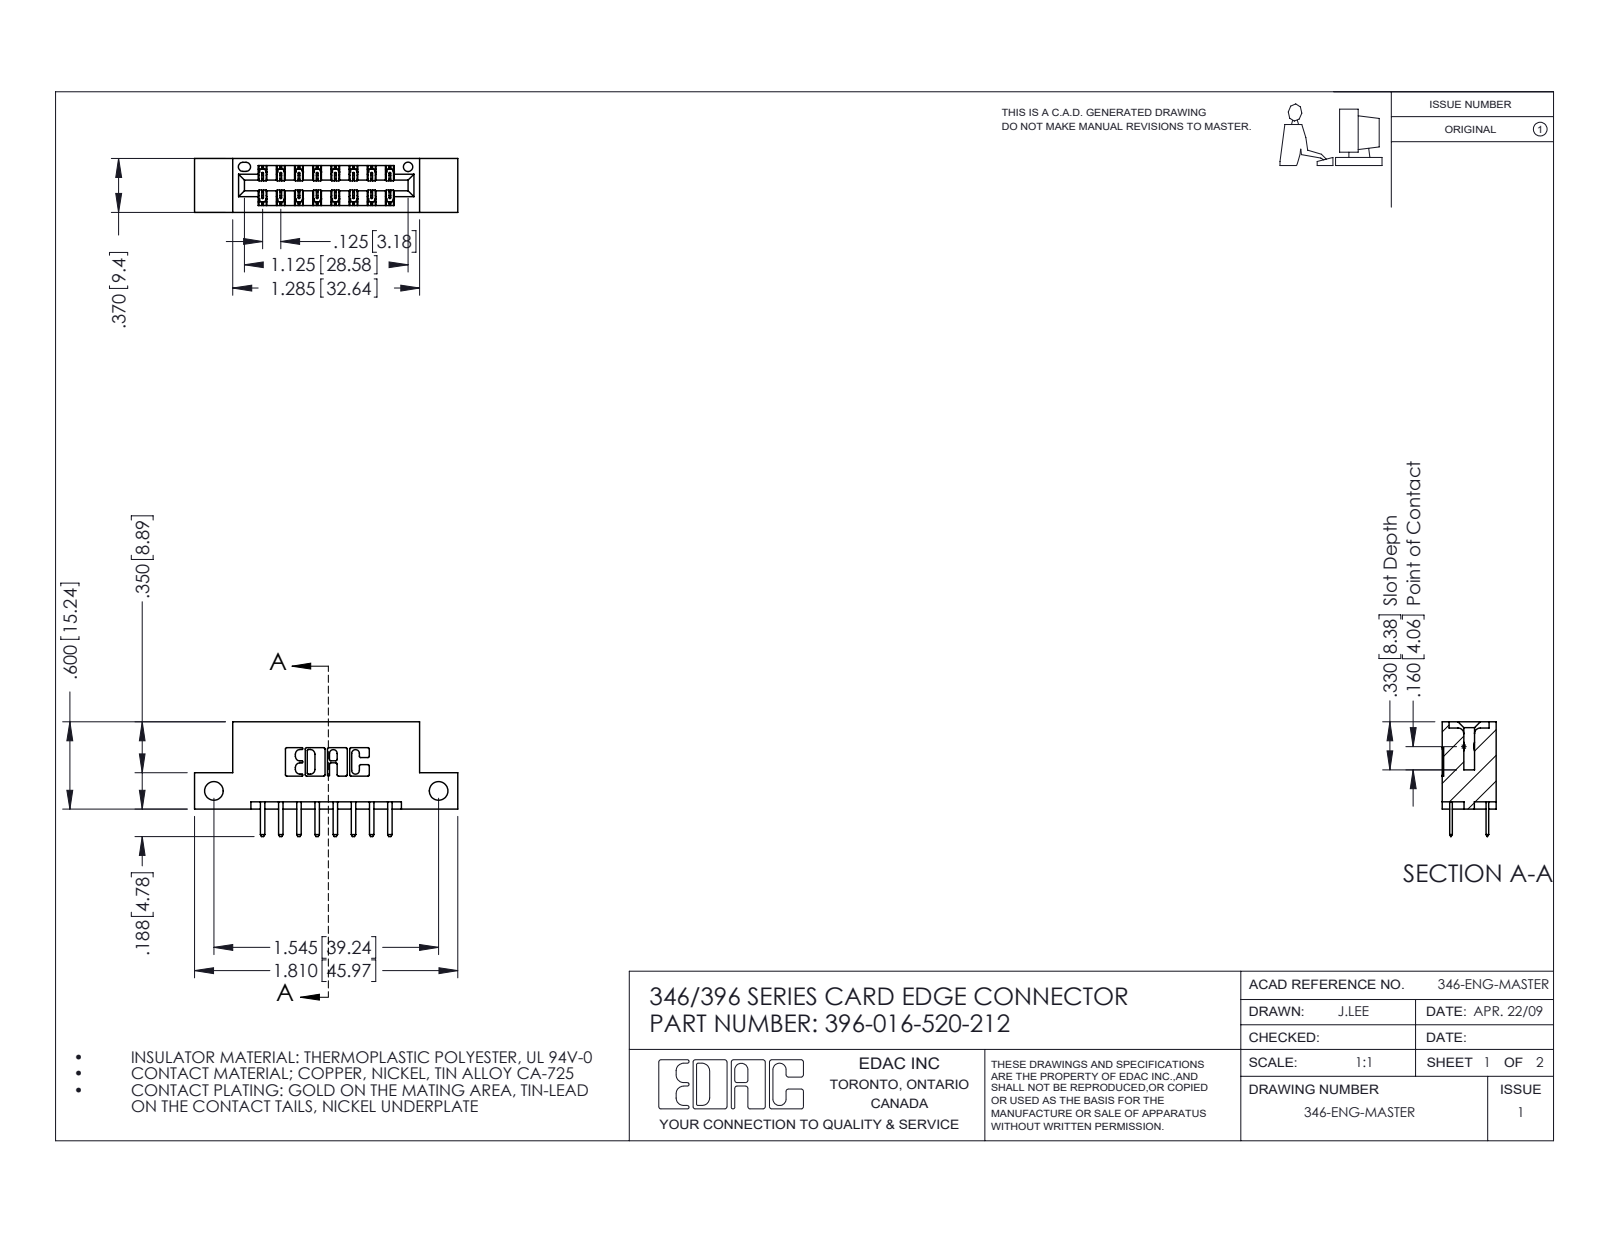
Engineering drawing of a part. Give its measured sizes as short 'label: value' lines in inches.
name: 396-016-520-212; 346 Part_Flush Mounting Lugs - Side Mount; 345-292-001_345-293-120
written by: SolidWorks 2016 (CONFIG_CONTROL_DESIGN)
unit: in
bodies: 17 solids, 1018 faces (668 planar, 350 cylindrical, 0 other)
size: 1.81 × 0.788 × 0.37
volume: 0.252 in³; area: 7.721 in²
holes: 2× ⌀0.128, 1× ⌀0.064
rounds: 24× R0.006, 22× R0.01, 20× R0.01, 6× R0.007, 6× R0.031, 3× R0.026, 2× R0.014, 2× R0.022
face distances: 0.25, 0.048, 0.322, 0.37, 0.5, 0.148, 0.222, 0.1, 0.174, 0.125
hole spacings: 1.545
